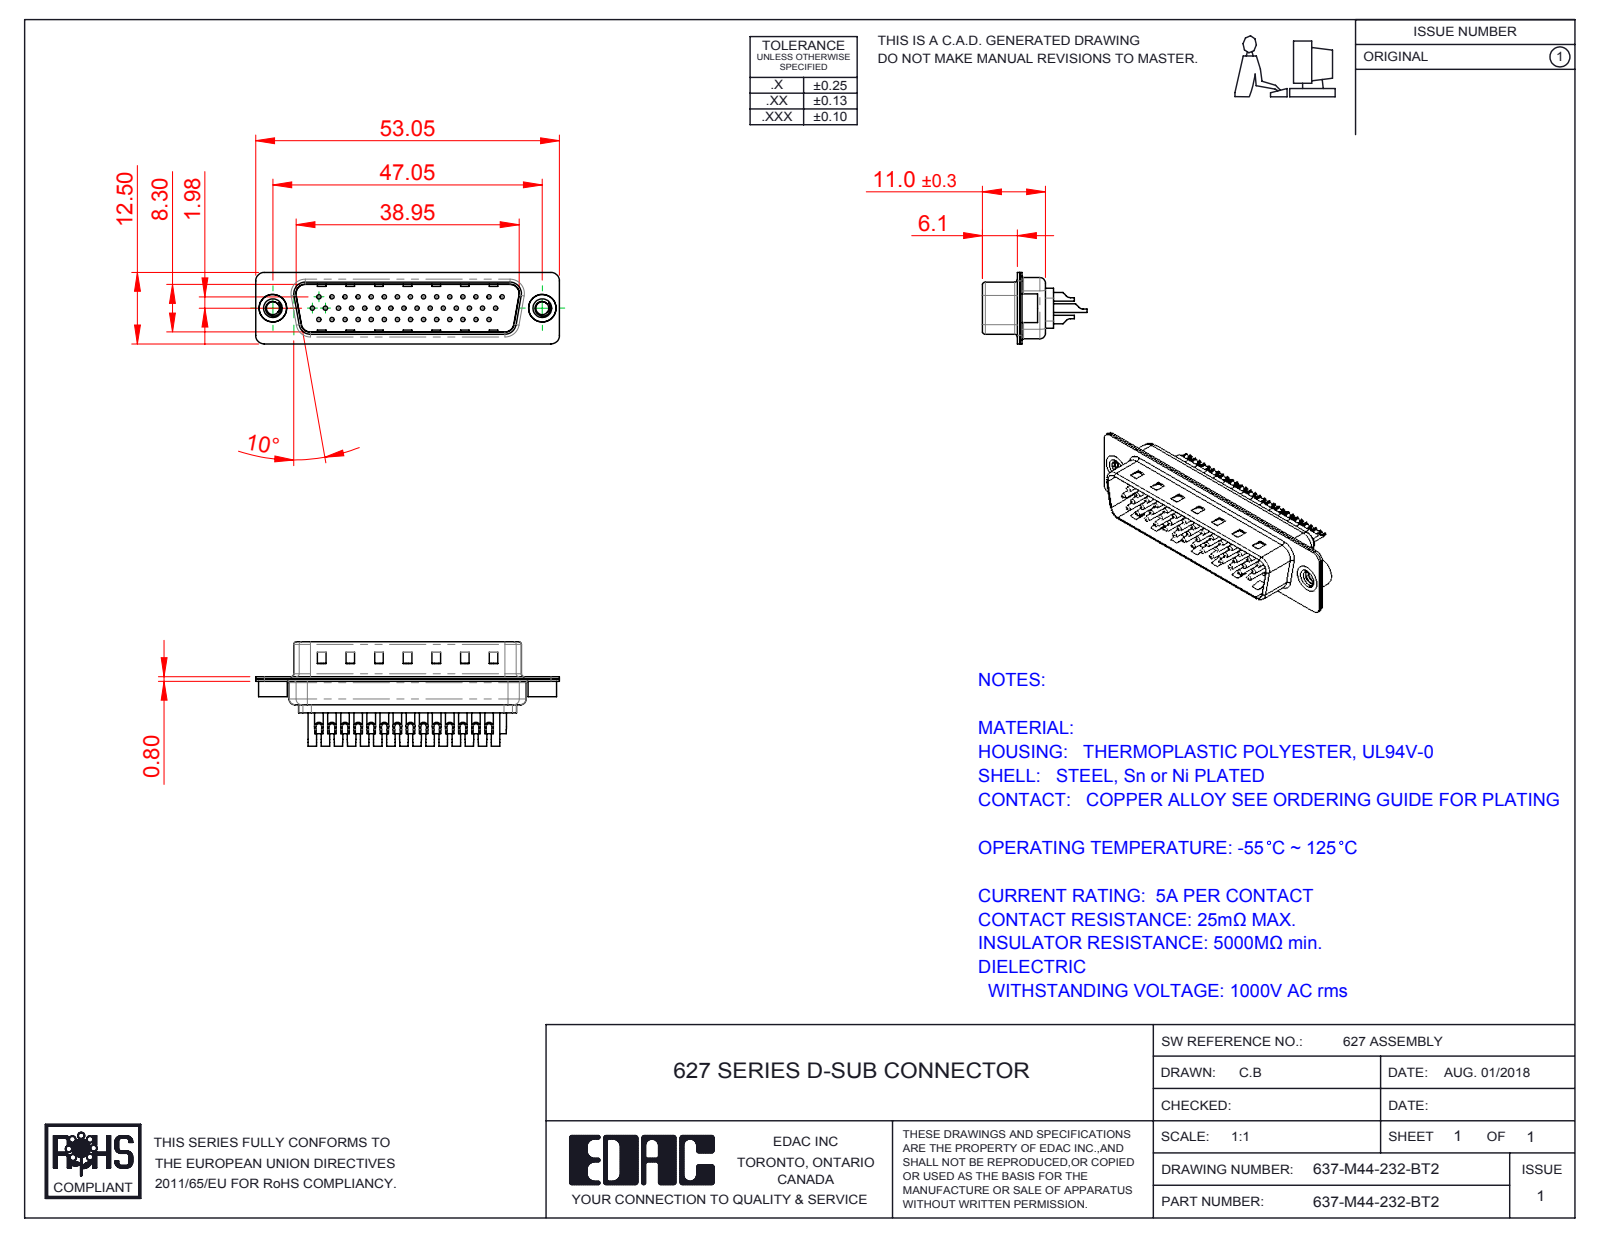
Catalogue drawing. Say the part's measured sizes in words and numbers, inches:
The part is named "637M Shell Front_44 Contacts; 637-M44-232-BT2; 637M Housing_44 Contacts; 637M 4-40 Threaded Rivet (+4 more)". Its 3-D file was written by "SolidWorks 2016 (CONFIG_CONTROL_DESIGN)". It is 49 solids with 2004 faces: 567 planar, 841 cylindrical and 596 other. Overall it measures 2.089 by 0.719 by 0.492 inches. Its volume is 0.181 cubic inches and its surface area 13.97 square inches. Round holes: 44 of diameter 0.03, 44 of diameter 0.039, 44 of diameter 0.063, 44 of diameter 0.079, 2 of diameter 0.089, 2 of diameter 0.157, 2 of diameter 0.189. Round bosses or shafts: 44 of diameter 0.059, 3 of diameter 0.079, 3 of diameter 0.03, 2 of diameter 0.197, 2 of diameter 0.193. Partial cylindrical surfaces (rounded edges, fillets, slot ends): 16 of radius 0.059, 12 of radius 0.079, 8 of radius 0.02, 8 of radius 0.063, 7 of radius 0.039, 4 of radius 0.01, 4 of radius 0.024, 4 of radius 0.026. The main face-to-face distances are 0.016, 0.031, 0.374, 0.358, 0.343, 0.39, 0.03, 0.014, 0.043, 0.047. The hole center spacings are 0.09, 0.156, 0.09, 0.18, 0.324, 0.27, 0.45, 0.59.
